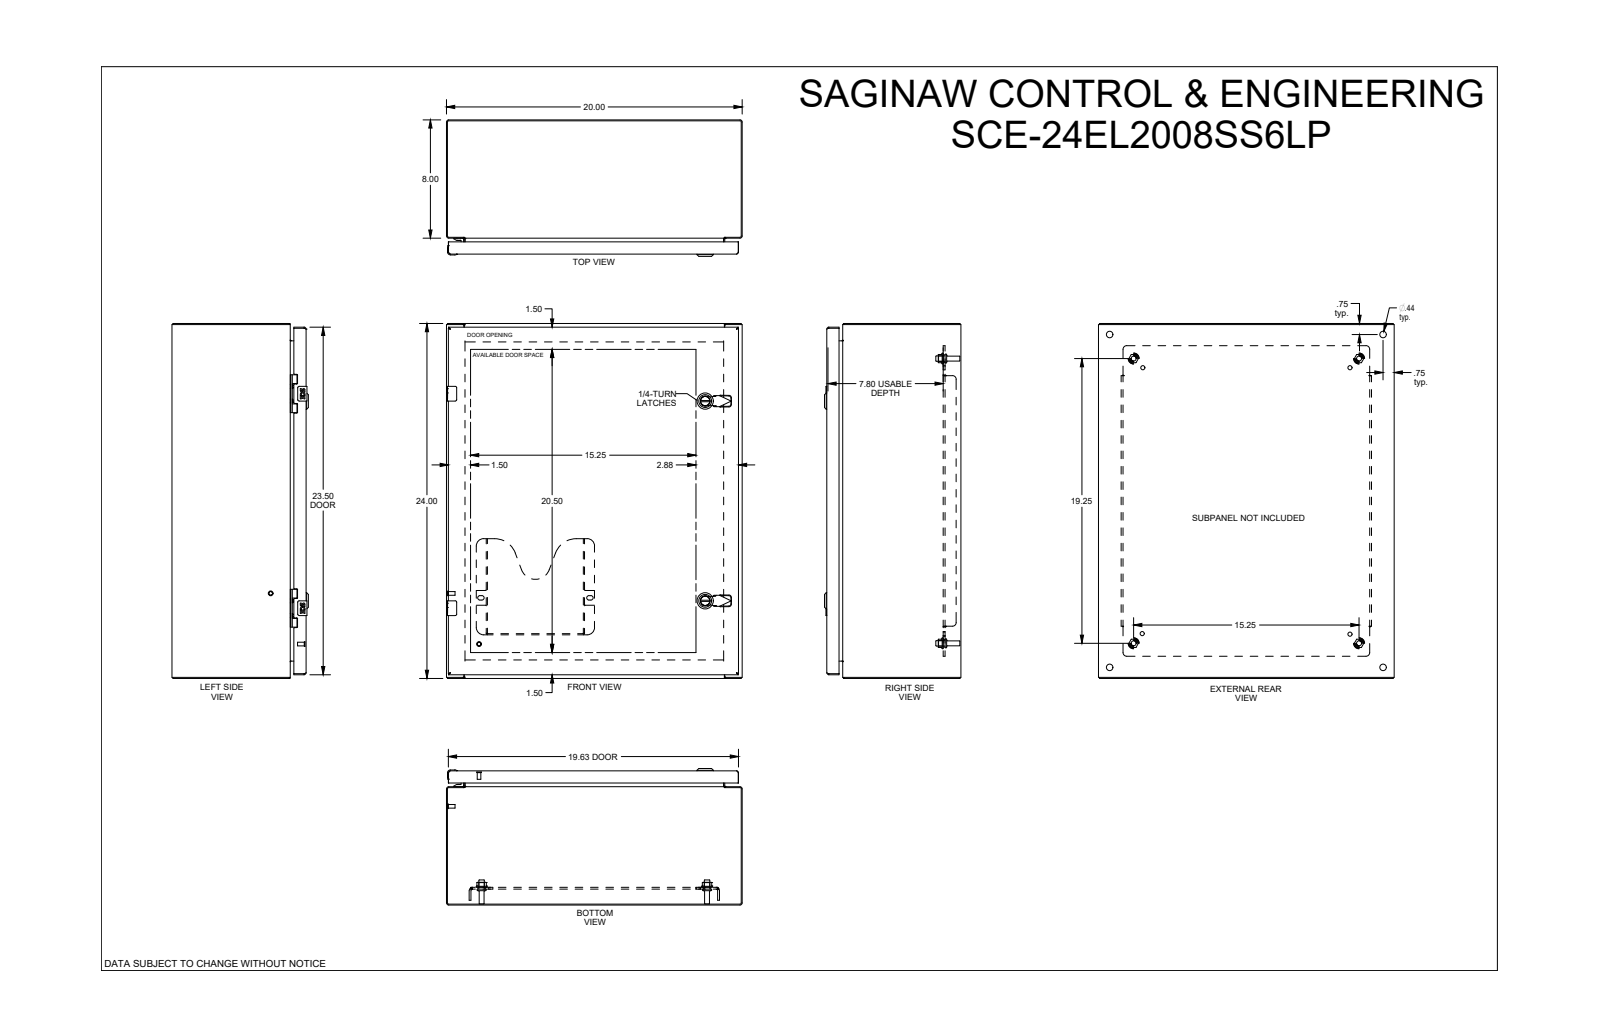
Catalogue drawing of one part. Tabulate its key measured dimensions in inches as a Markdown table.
| quantity | value |
| --- | --- |
| part name | SCE-24EL2008SS6LP |
| STEP written by | SolidWorks 2019 (CONFIG_CONTROL_DESIGN) |
| units | inches |
| bodies | 0 solids, 2806 faces (1297 planar, 749 cylindrical, 760 other) |
| overall size | 24 × 20 × 9.23 |
| round holes (diameter × count) | 0.172 × 4, 0.205 × 4, 0.244 × 4, 0.266 × 4, 0.281 × 4, 0.367 × 4, 0.375 × 4, 0.437 × 4, 0.5 × 4, 0.156 × 2, 0.197 × 2, 0.218 × 2 |
| round bosses / shafts (diameter × count) | 0.17 × 6, 0.366 × 4, 0.332 × 4, 0.25 × 4, 0.248 × 4, 0.196 × 3, 1.102 × 2, 0.866 × 2 |
| partial cylindrical surfaces (radius × count) | 0.012 × 56, 0.015 × 32, 0.01 × 28, 0.04 × 23, 0.02 × 20, 0.029 × 12, 0.07 × 10, 0.145 × 10 |
| main face-to-face distances | 0.075, 0.075, 8.923, 8.998, 9.073, 8.998, 0.125, 19.925, 1, 7.923 |
| hole center spacings | 14.5, 0.985, 0.02, 0.875, 2.298, 4.493, 16.953, 20.938 |
